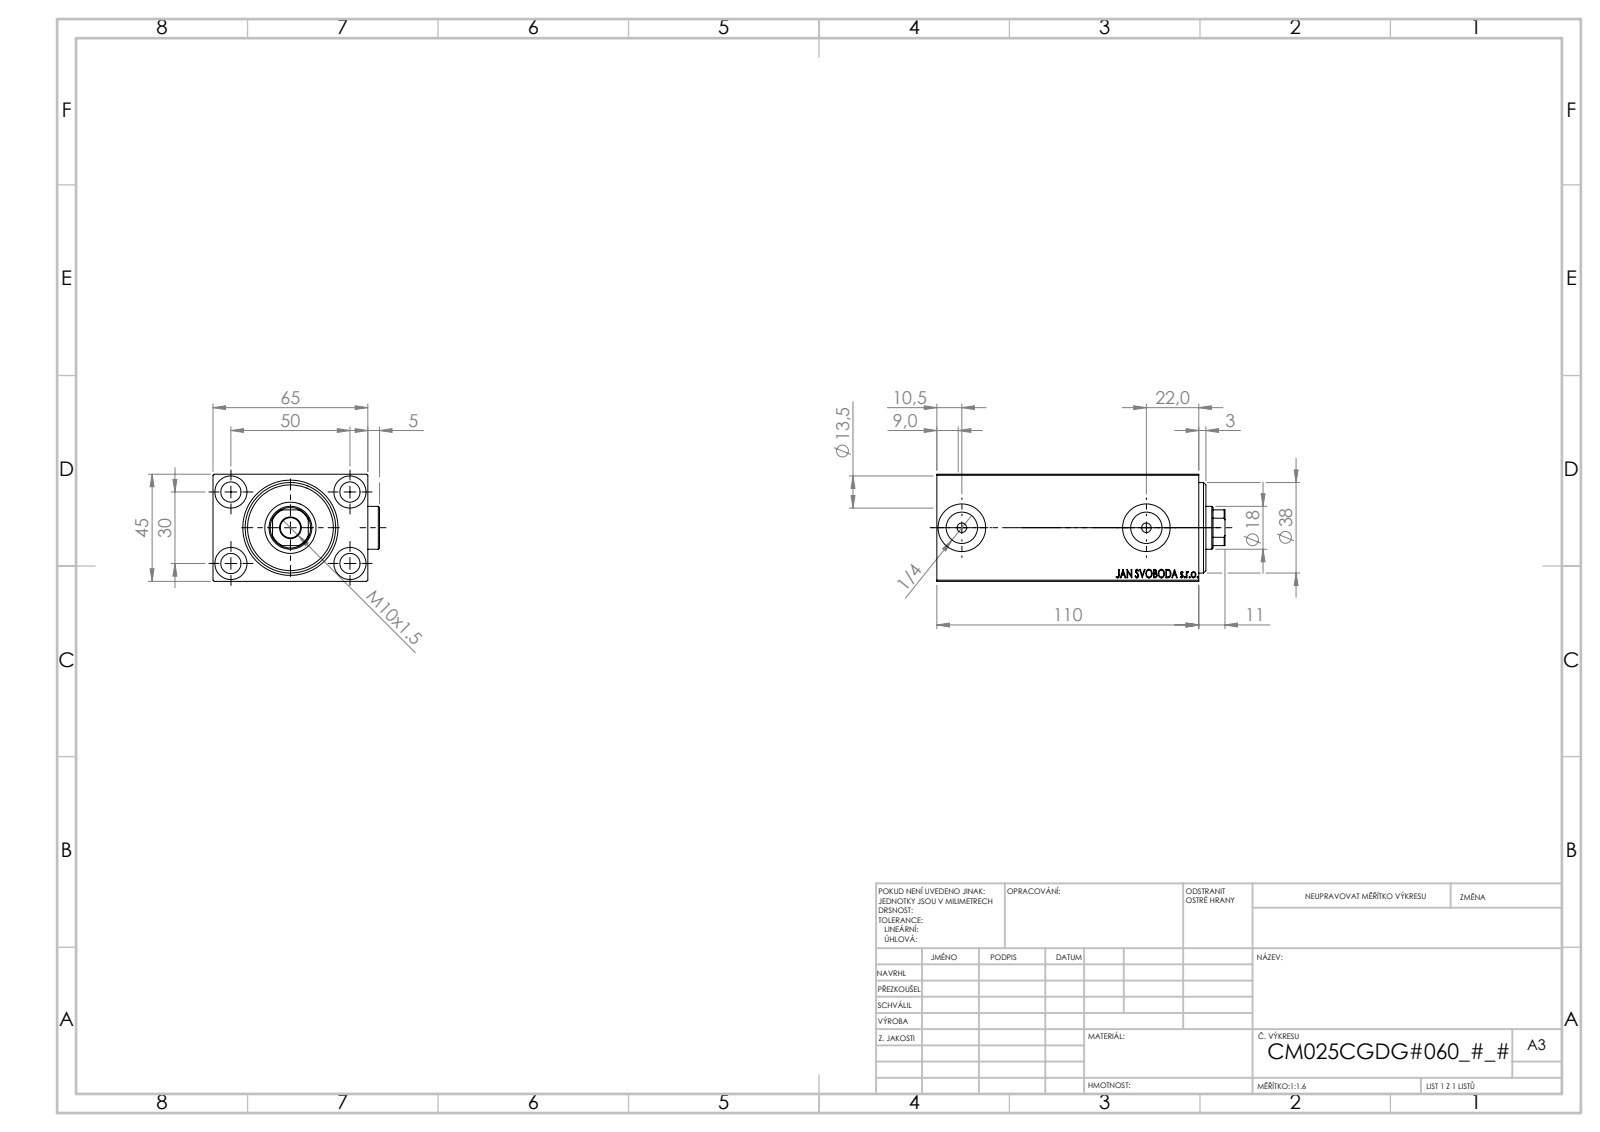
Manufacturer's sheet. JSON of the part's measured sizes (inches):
{"part_name": "Zatka_OIL_PORT; V450CM_C_Body; V450CM_VC_B; V450CM_C_VCP", "step_written_by": "SolidWorks 2019 (CONFIG_CONTROL_DESIGN)", "units": "inches", "bodies": {"solids": 5, "faces": 916, "planar": 442, "cylindrical": 76, "other": 398}, "overall_size": [4.764, 2.752, 1.772], "volume_in3": 16.79, "surface_area_in2": 104.6, "round_holes": [[0.335, 5], [0.531, 4], [0.157, 2], [0.518, 2], [0.787, 2], [0.709, 1], [0.846, 1], [0.984, 1], [1.063, 1], [1.496, 1]], "round_bosses_or_shafts": [[0.709, 2]], "partial_cylinders_radius": [[0.335, 1]], "face_to_face_distances": [1.772, 2.559, 0.197, 0.236, 3.898, 4.094, 2.555, 4.134, 4.331, 0.118], "hole_center_spacings": [1.148, 1.181, 1.969, 2.296, 3.051]}
